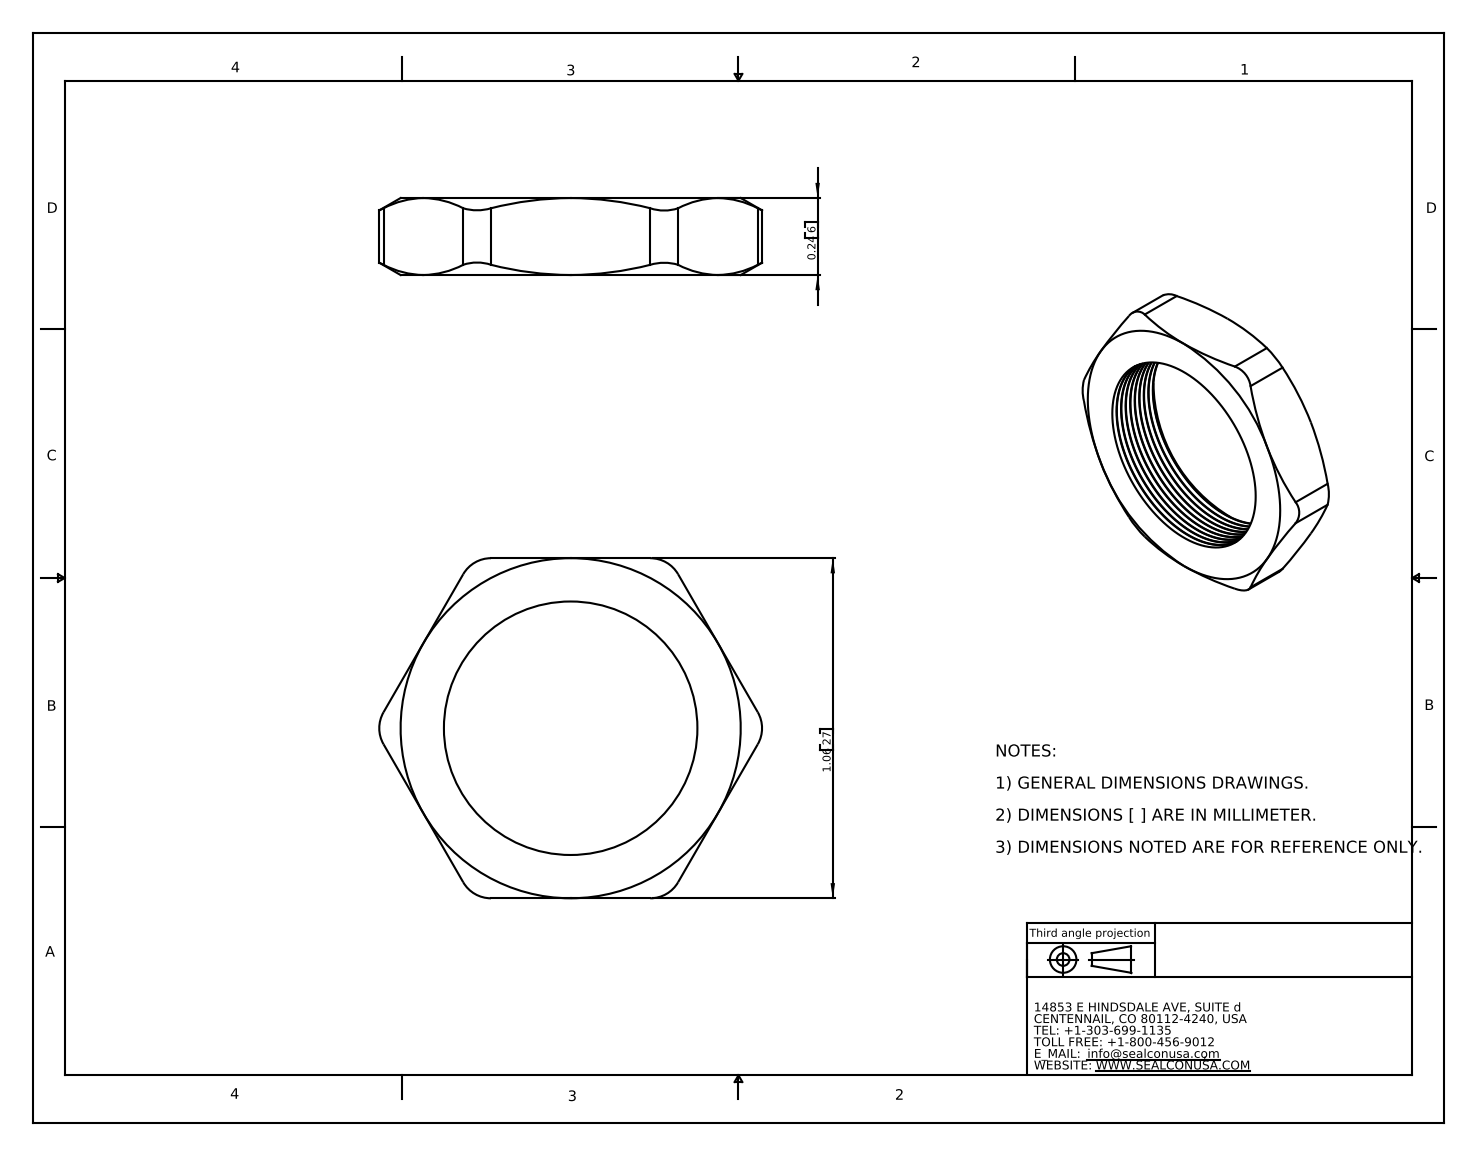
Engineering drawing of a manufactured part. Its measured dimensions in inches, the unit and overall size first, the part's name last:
Units: inches
Overall size (bounding box): 1.193 × 1.06 × 0.24
Round holes (diameter × count): ⌀0.79 ×1
Partial cylindrical surfaces — rounded edges, fillets, slot ends (radius × count): R0.1 ×6
Main face-to-face distances: 0.24, 1.06
Volume: 0.107 in³ · Surface area: 2.884 in²
Bodies: 1 solid, 87 faces (8 planar, 25 cylindrical, 54 other)
Part name (STEP PRODUCT): NM-20
STEP written by: SolidWorks 2007 (CONFIG_CONTROL_DESIGN)
